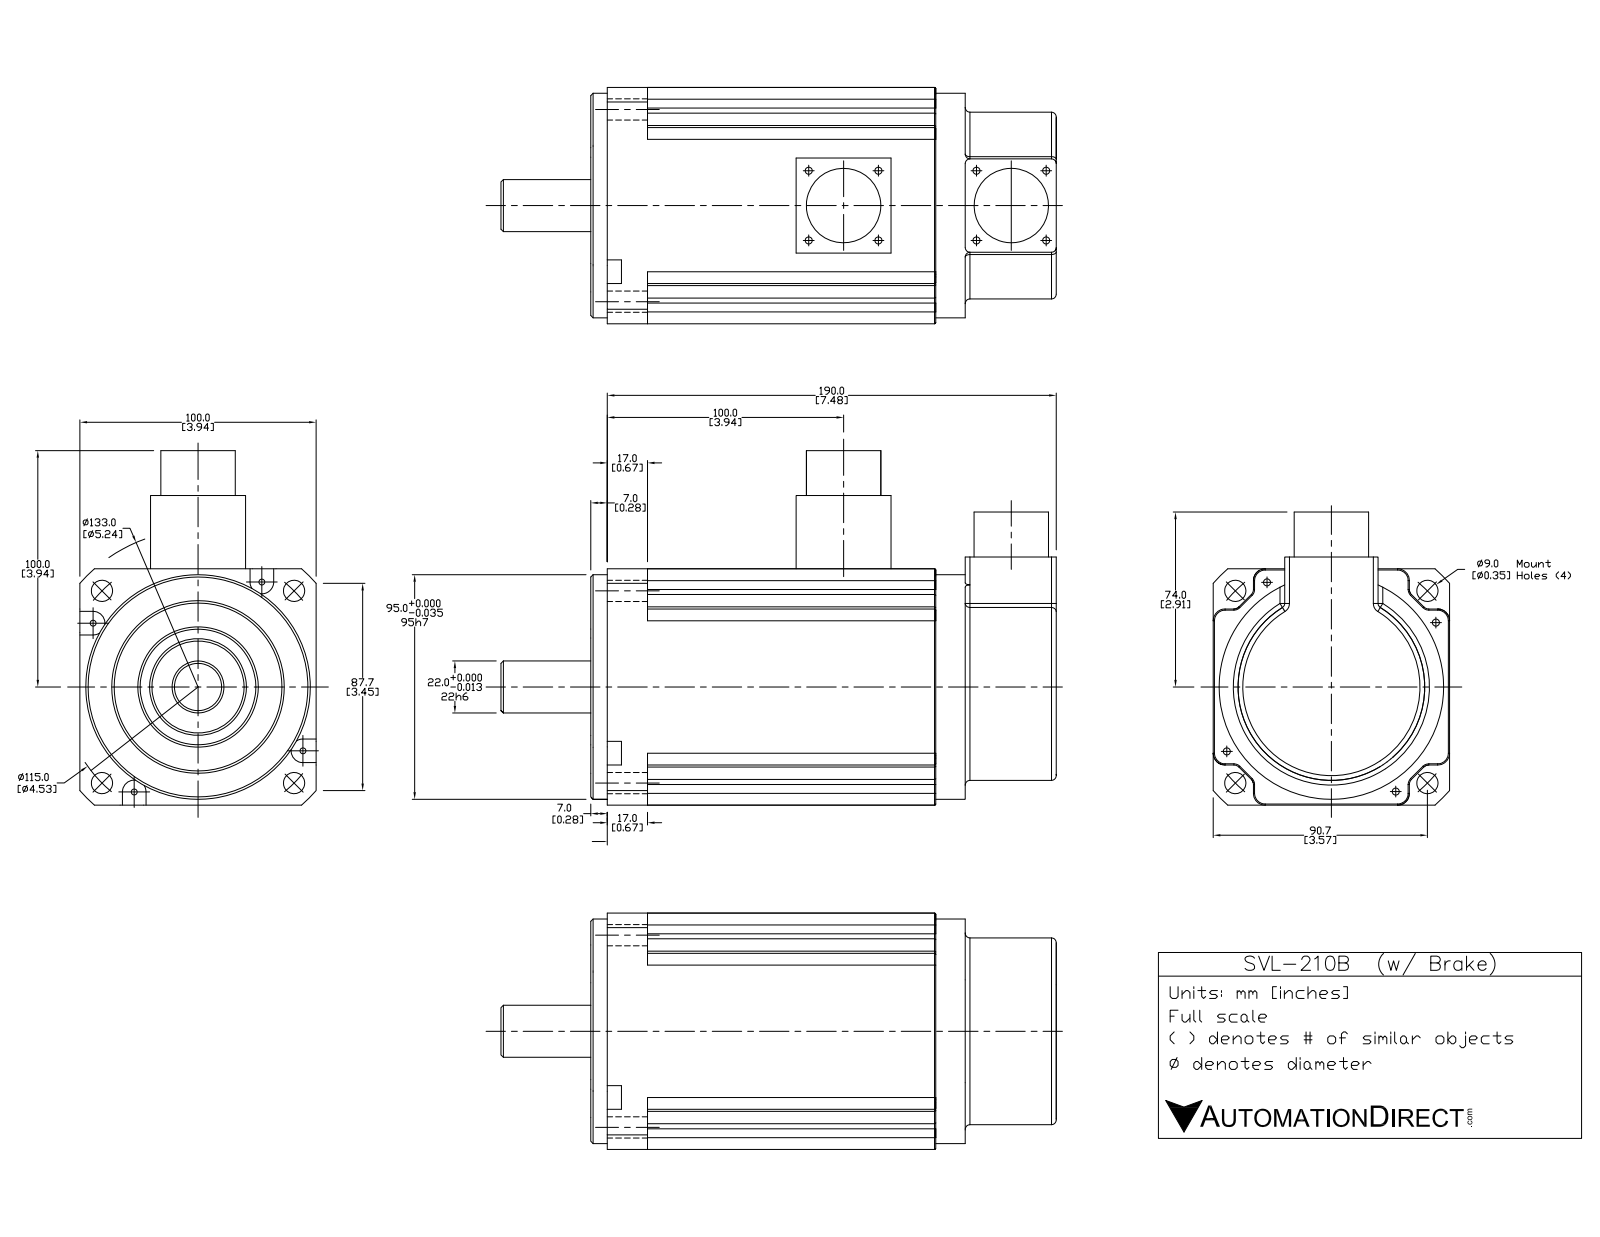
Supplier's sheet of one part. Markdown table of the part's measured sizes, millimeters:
| quantity | value |
| --- | --- |
| part name | SVL-210B |
| STEP written by | SolidWorks 2015 (AUTOMOTIVE_DESIGN) |
| units | millimeters |
| bodies | 36 solids, 433 faces (186 planar, 166 cylindrical, 81 other) |
| overall size | 235 × 150 × 100 |
| volume | 1 668 000 mm³ |
| surface area | 147 836 mm² |
| round holes (diameter × count) | 9 × 4, 27 × 1, 27.2 × 1, 72 × 1 |
| round bosses / shafts (diameter × count) | 2 × 17, 8 × 8, 1.5 × 6, 2.5 × 3, 31.5 × 2, 95 × 1, 83 × 1, 50 × 1 |
| partial cylindrical surfaces (radius × count) | 5 × 20, 2 × 4, 4 × 4, 66.5 × 1 |
| main face-to-face distances | 110.5, 100, 26, 17, 136.5, 19, 7, 129.5, 60.5, 171 |
| hole center spacings | 57.5, 81.32, 115, 71.35 |
